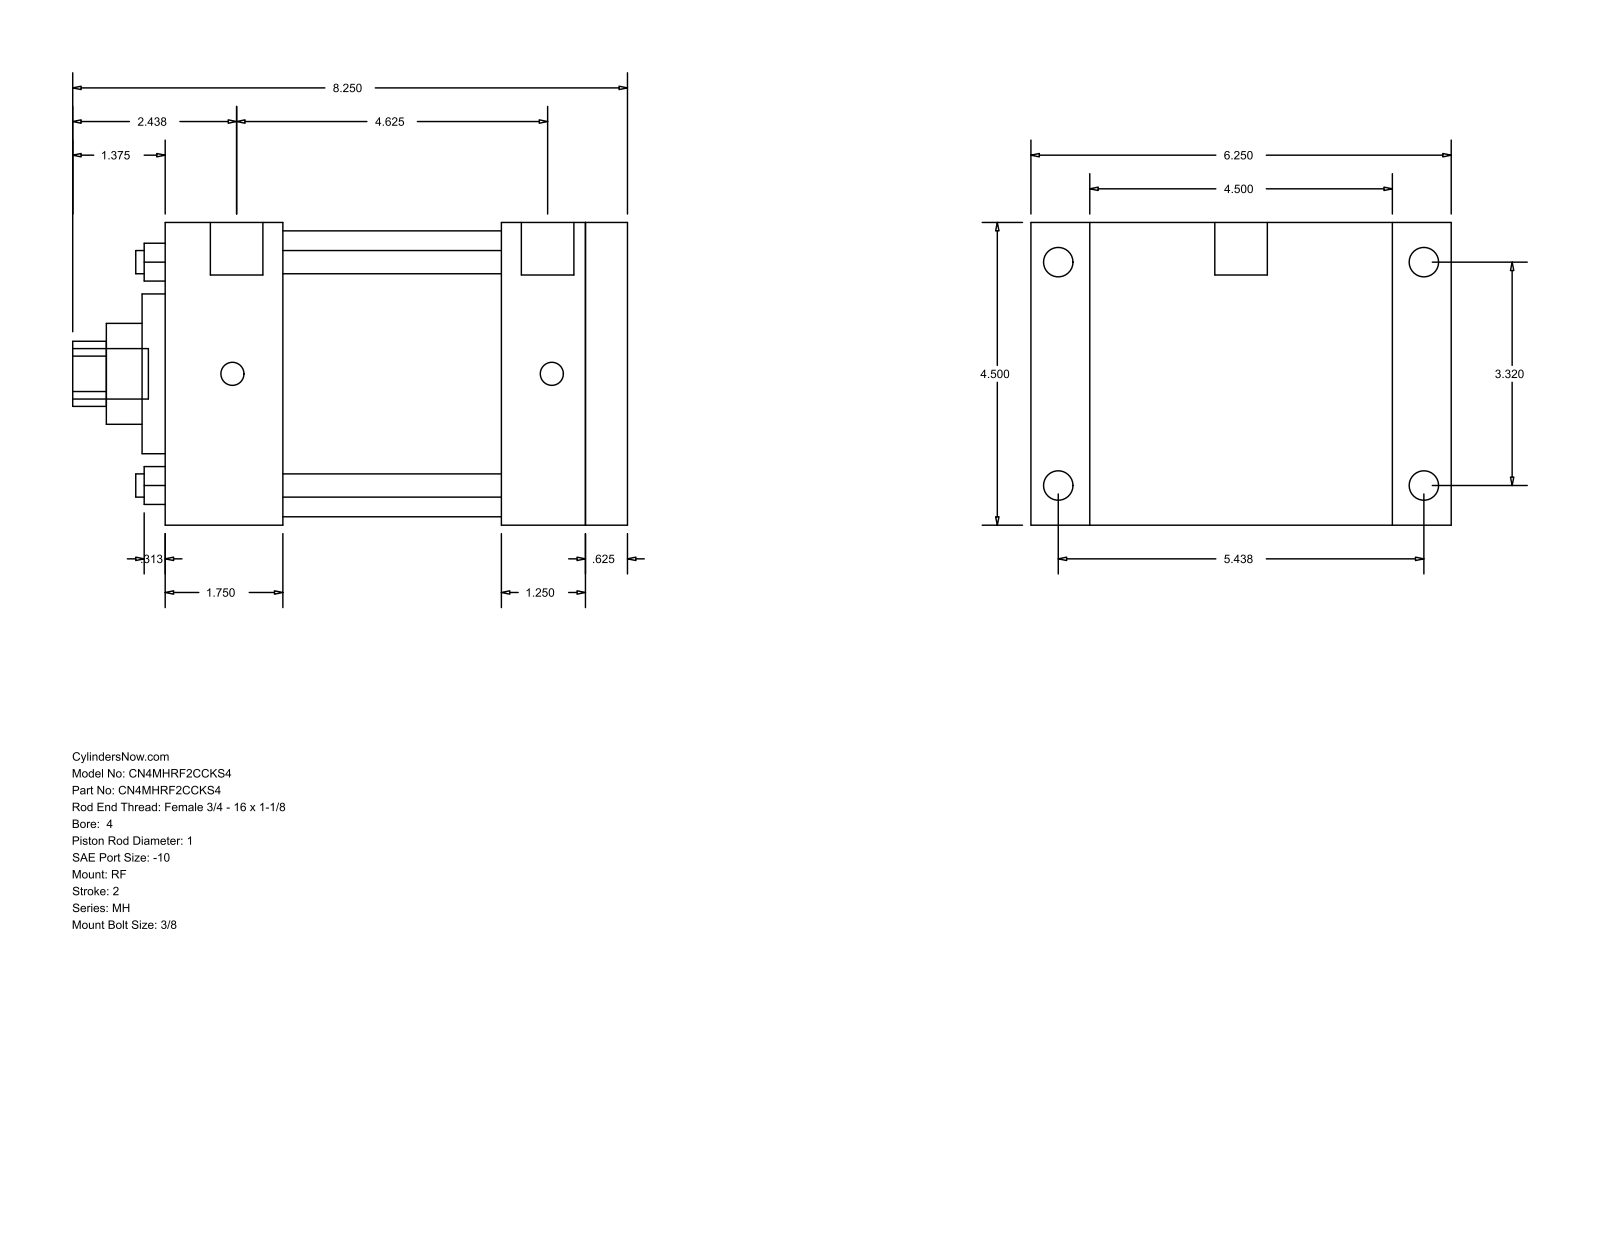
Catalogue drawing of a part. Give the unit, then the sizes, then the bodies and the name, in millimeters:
Units: millimetres
Overall size (bounding box): 209.55 × 158.75 × 114.3
Round holes (diameter × count): ⌀8.76 ×4, ⌀25.4 ×1, ⌀38.1 ×1, ⌀60.33 ×1, ⌀107.95 ×1
Round bosses / shafts (diameter × count): ⌀11.13 ×4, ⌀8.73 ×4, ⌀19.84 ×2, ⌀19.05 ×1
Partial cylindrical surfaces — rounded edges, fillets, slot ends (radius × count): R12.29 ×1
Main face-to-face distances: 114.3, 174.63, 158.76, 15.87, 44.46, 130.17, 127.01, 82.55, 31.75, 47.62
Hole centre spacings: 59.62, 84.32, 119.25
Bodies: 0 solids, 94 faces (65 planar, 29 cylindrical, 0 other)
Part name (STEP PRODUCT): MH_RF__0400_1
STEP written by: GSSL Pune (CONFIG_CONTROL_DESIGN)
